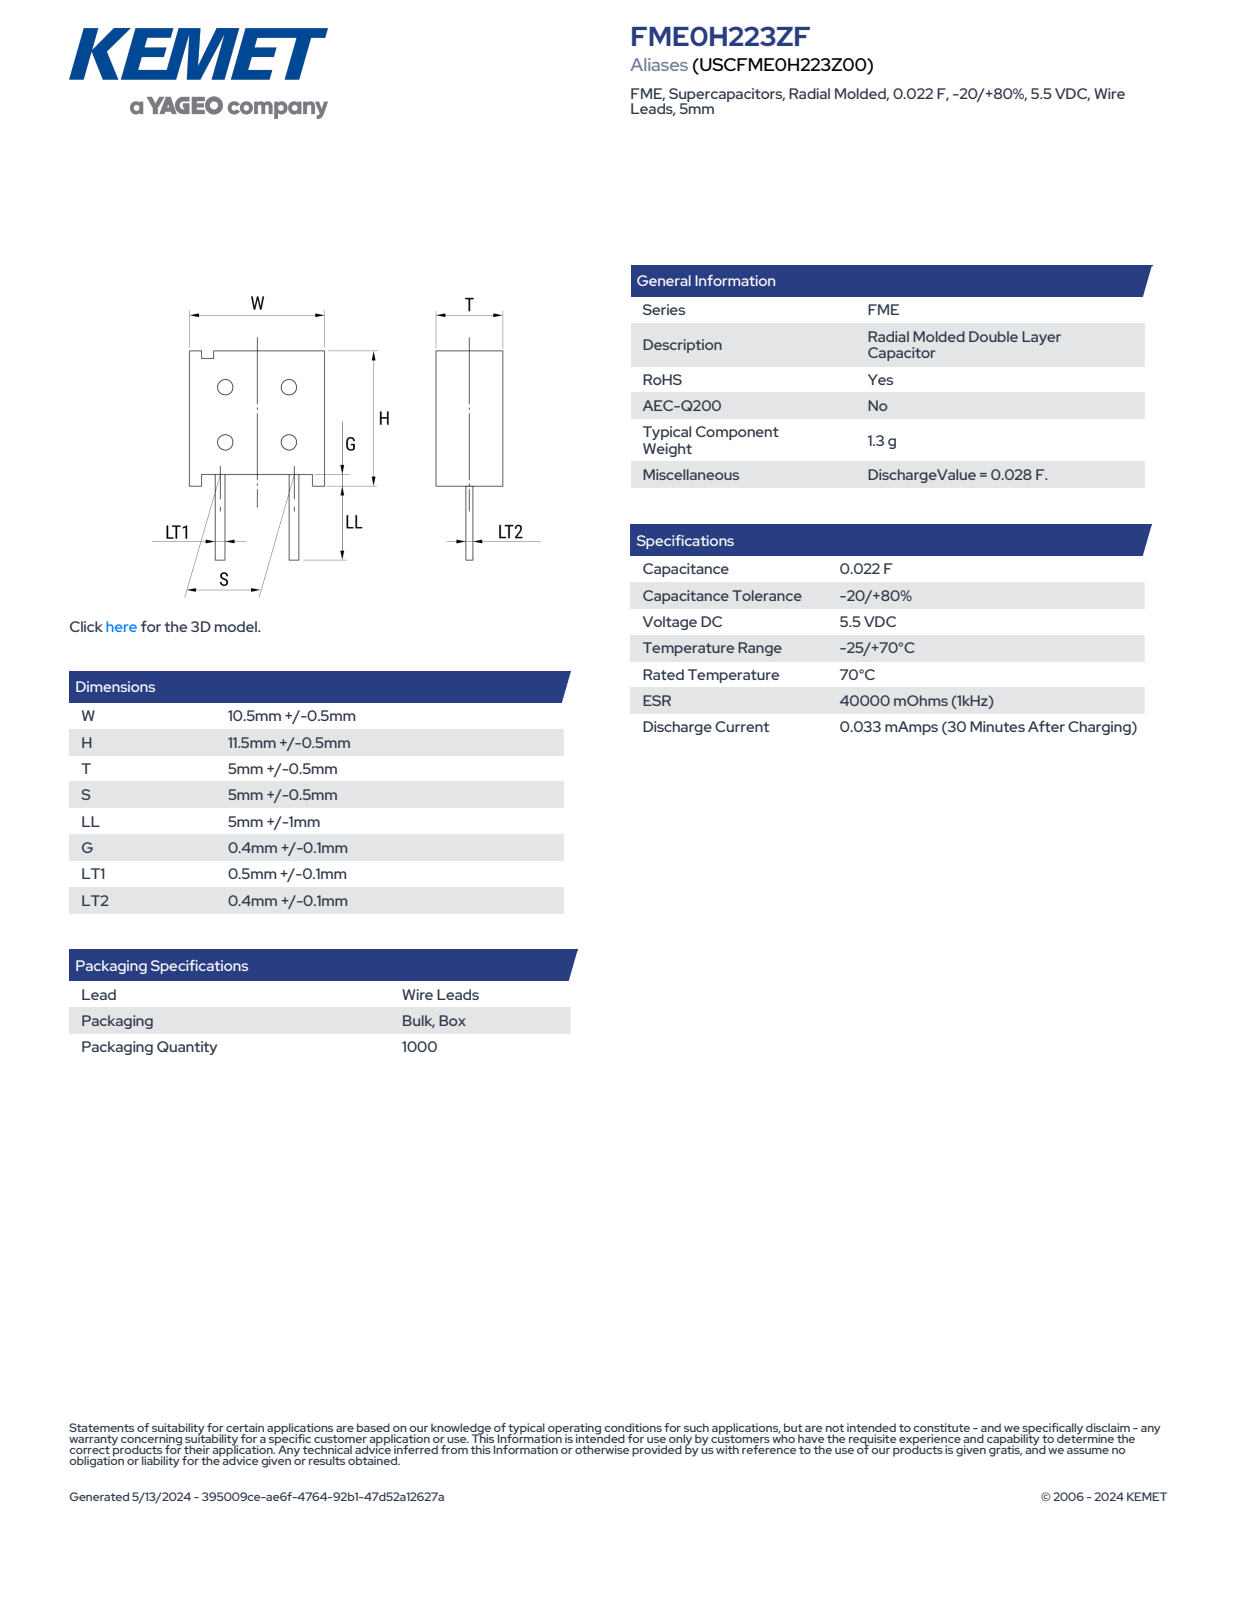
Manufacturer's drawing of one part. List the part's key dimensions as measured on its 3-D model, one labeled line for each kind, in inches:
Part name (STEP PRODUCT): CDR_RM_W11H12T5.5S5LL6G0.5LT10.6LT20.5
STEP written by: SolidWorks 2014 (AUTOMOTIVE_DESIGN)
Units: inches
Bodies: 4 solids, 79 faces (77 planar, 2 cylindrical, 0 other)
Overall size (bounding box): 0.709 × 0.433 × 0.217
Volume: 0.043 in³ · Surface area: 0.877 in²
Partial cylindrical surfaces — rounded edges, fillets, slot ends (radius × count): R0.02 ×2
Main face-to-face distances: 0.217, 0.433, 0.453, 0.098, 0.118, 0.02, 0.197, 0.106, 0.327, 0.13
